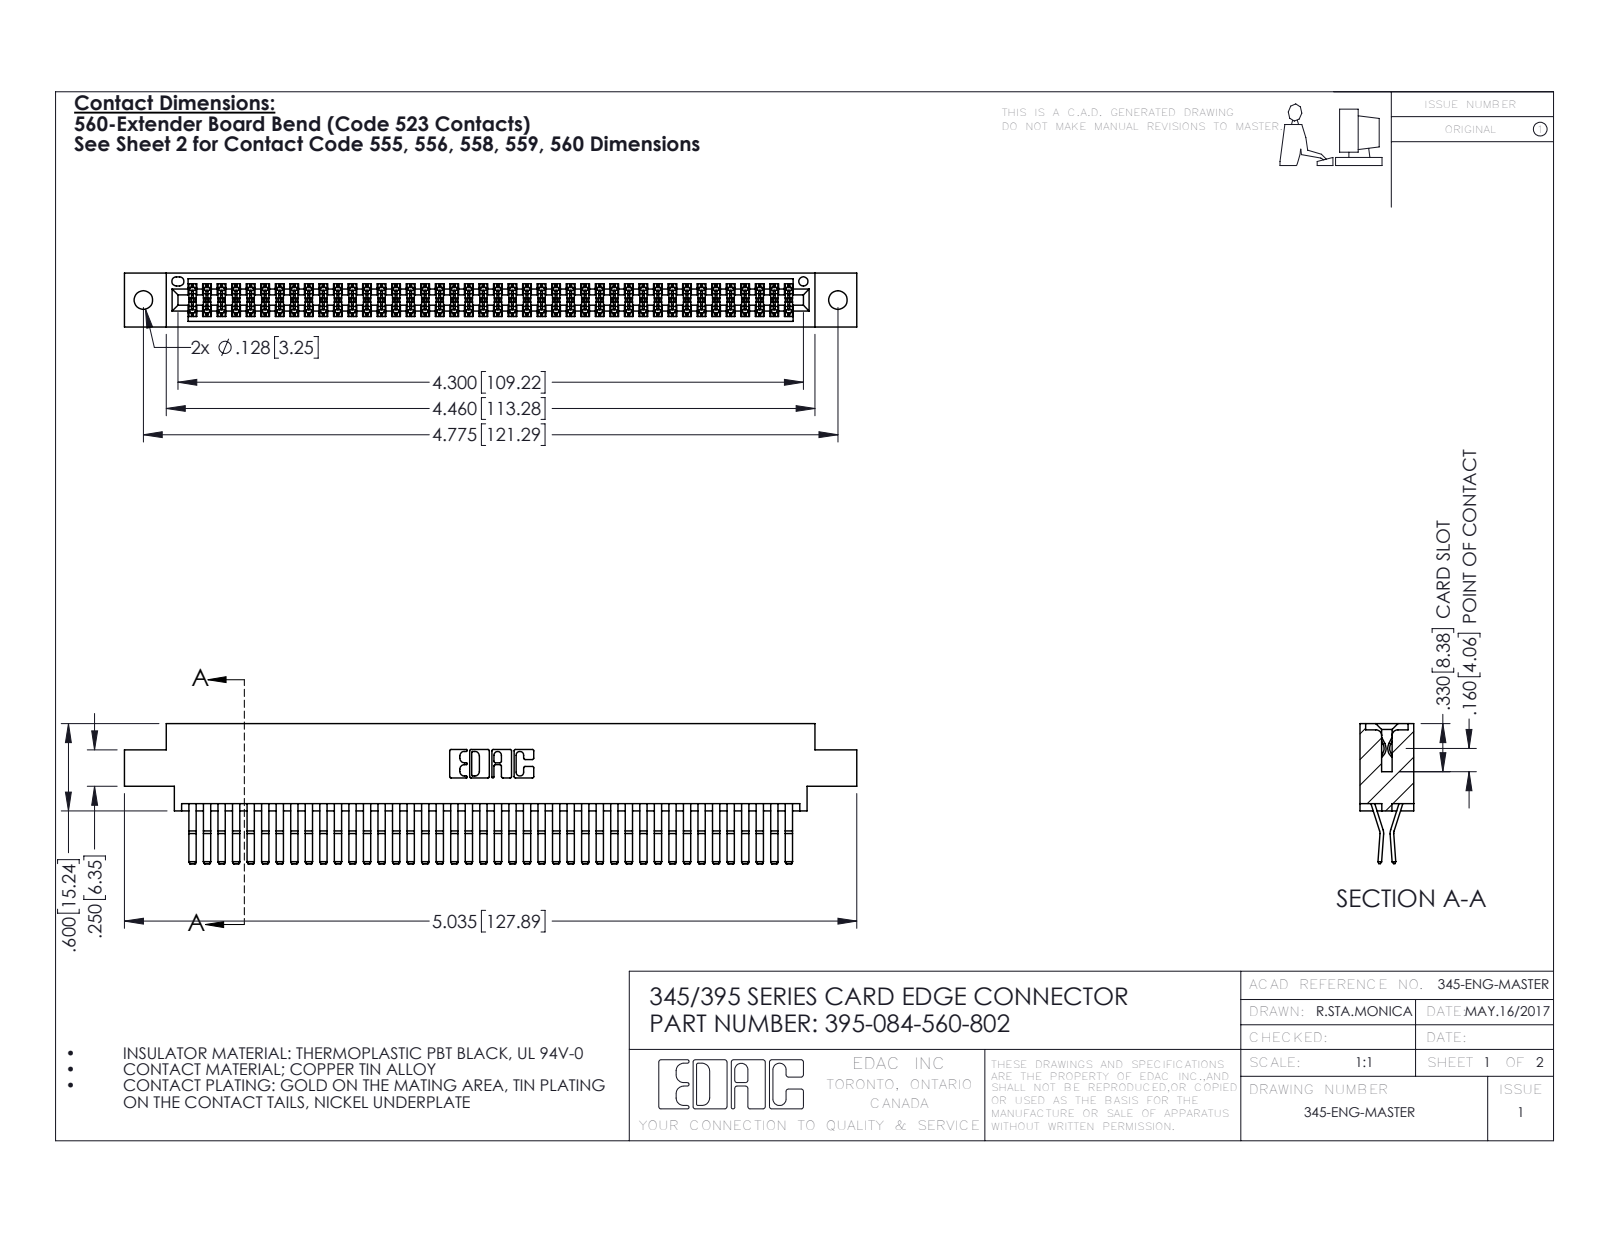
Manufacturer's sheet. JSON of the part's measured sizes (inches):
{"part_name": "345 Part_0.170 Offset - 0.128 Dia; 395-084-560-802; 345-292-001_560 Tail", "step_written_by": "SolidWorks 2016 (CONFIG_CONTROL_DESIGN)", "units": "inches", "bodies": {"solids": 85, "faces": 4498, "planar": 2856, "cylindrical": 1642, "other": 0}, "overall_size": [5.035, 0.962, 0.37], "volume_in3": 0.783, "surface_area_in2": 31.38, "round_holes": [[0.128, 2], [0.064, 1]], "partial_cylinders_radius": [[0.006, 127], [0.01, 22], [0.007, 6], [0.031, 6], [0.026, 3], [0.01, 2], [0.014, 2], [0.019, 2]], "face_to_face_distances": [0.025, 0.298, 0.072, 0.37, 0.2, 0.098, 0.272, 0.225, 0.175, 0.149], "hole_center_spacings": [0.27, 4.539, 4.775]}
